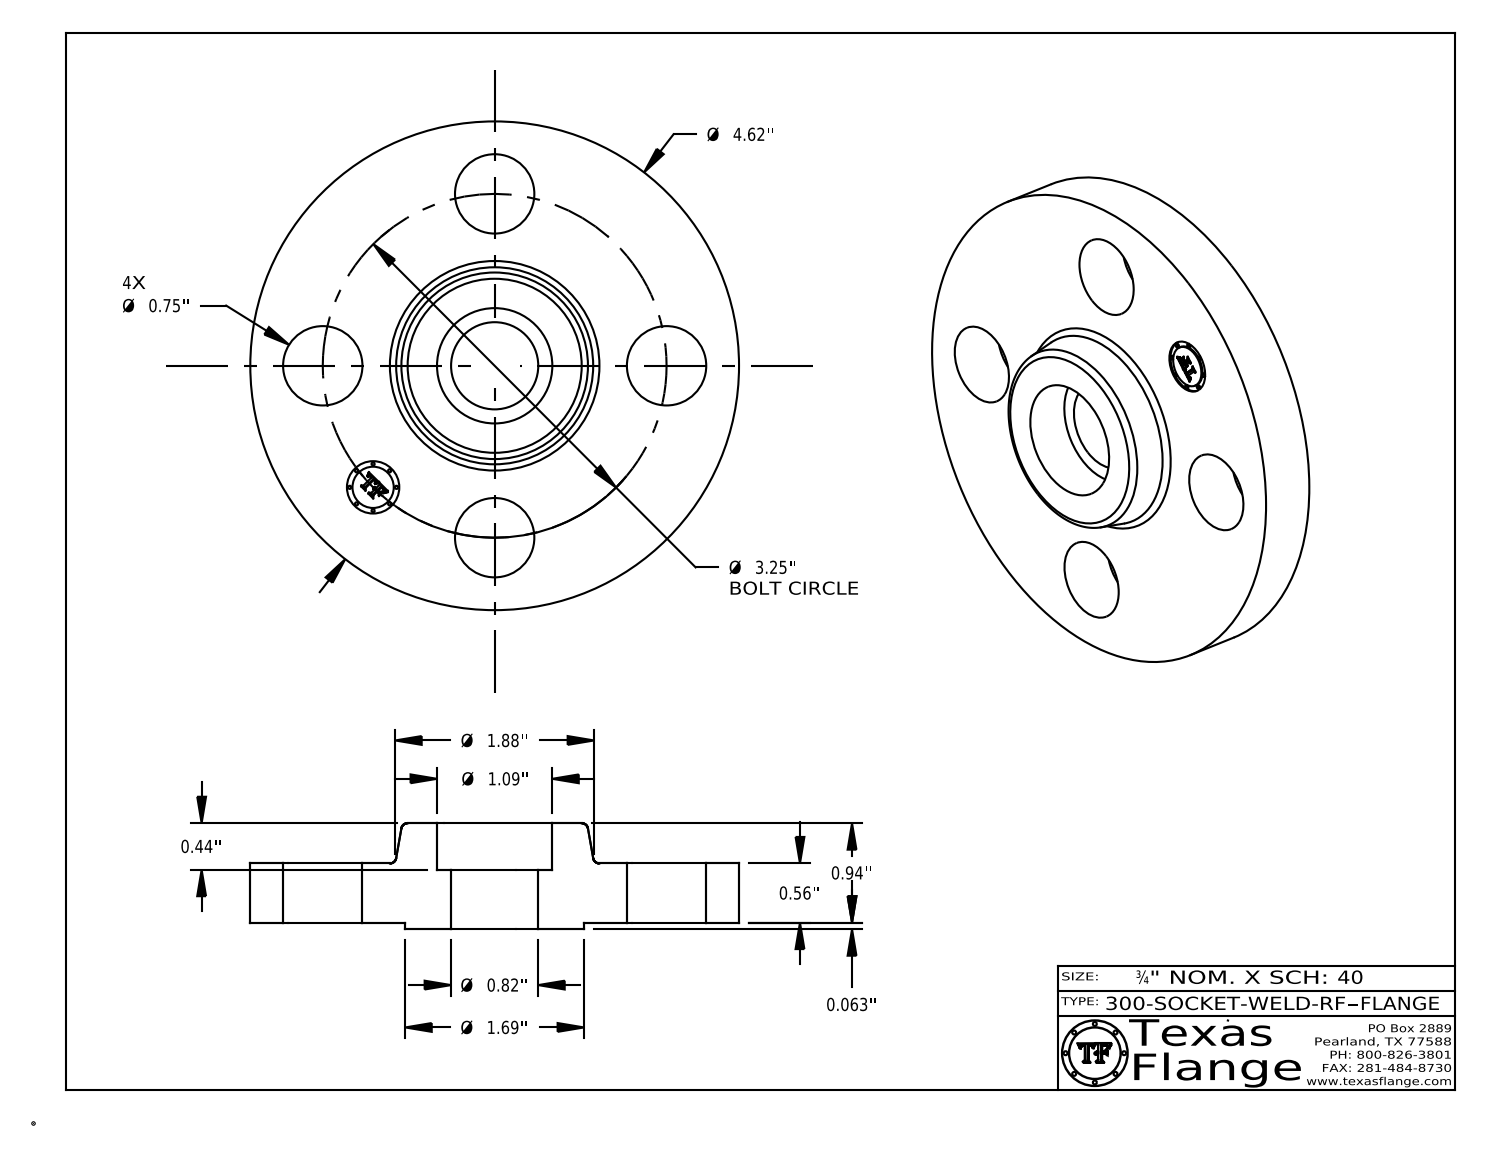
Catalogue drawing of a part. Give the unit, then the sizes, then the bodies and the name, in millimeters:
Units: millimetres
Overall size (bounding box): 117.3 × 117.3 × 25.5
Round holes (diameter × count): ⌀19.1 ×4, ⌀12.6 ×1, ⌀20.9 ×1, ⌀27.7 ×1
Round bosses / shafts (diameter × count): ⌀0.8 ×8, ⌀117.3 ×1, ⌀42.9 ×1, ⌀9.9 ×1
Main face-to-face distances: 14.2, 1.6, 15.8, 25.5, 23.9, 9.7, 14.3, 12.7, 1.5, 11.2
Hole centre spacings: 41.3, 58.4, 31.6, 76.3, 82.6
Volume: 144 300 mm³ · Surface area: 30 540 mm²
Bodies: 1 solid, 412 faces (370 planar, 36 cylindrical, 6 other)
Part name (STEP PRODUCT): 300-SOCKET-WELD-RF
STEP written by: CATIA V5 STEP AP214 (AUTOMOTIVE_DESIGN)
